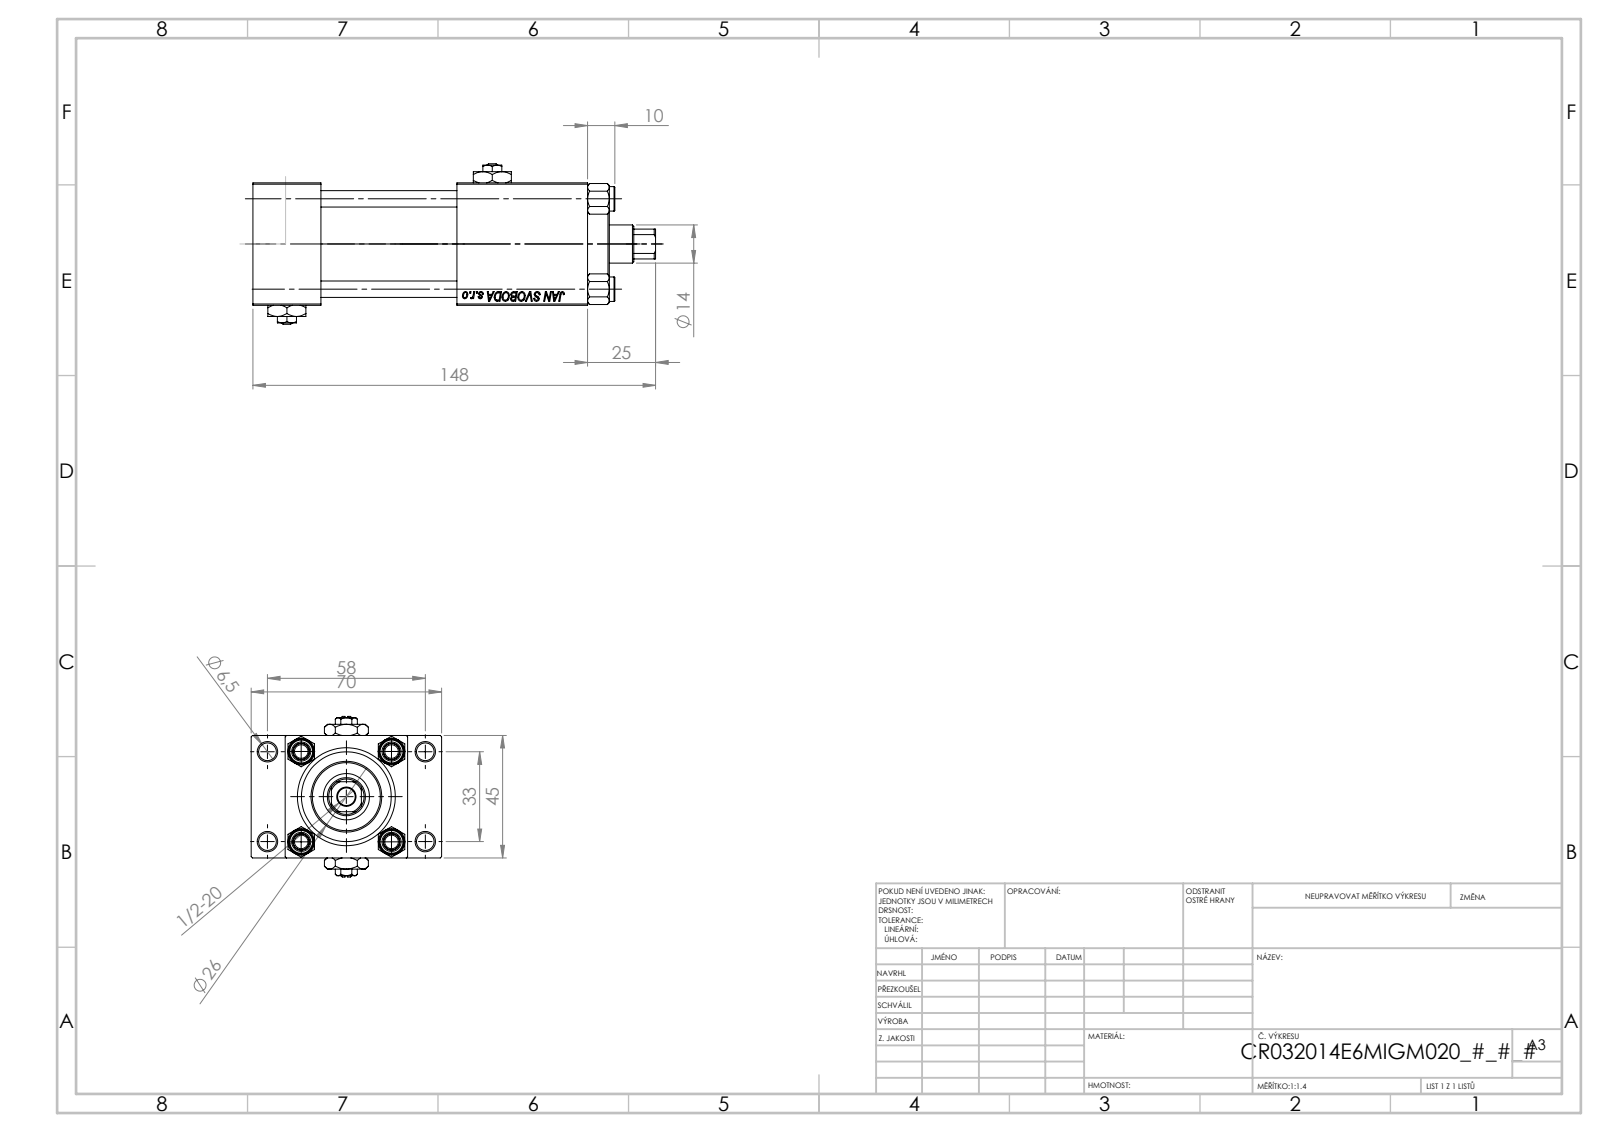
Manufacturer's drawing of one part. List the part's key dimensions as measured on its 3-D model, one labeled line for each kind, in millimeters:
Part name (STEP PRODUCT): V215_VC_A; V215CR_VCP_E; V215CR_TYCINKA_E; Zatka_pro_OIL_PORT (+2 more)
STEP written by: SolidWorks 2019 (CONFIG_CONTROL_DESIGN)
Units: millimetres
Bodies: 13 solids, 1229 faces (542 planar, 93 cylindrical, 594 other)
Overall size (bounding box): 148 × 70 × 59
Volume: 219 579 mm³ · Surface area: 78 015 mm²
Round holes (diameter × count): ⌀6.5 ×5, ⌀6 ×4, ⌀7 ×3, ⌀13.16 ×3, ⌀20 ×3, ⌀14 ×1, ⌀17 ×1, ⌀24 ×1, ⌀32 ×1, ⌀33 ×1
Round bosses / shafts (diameter × count): ⌀9 ×4, ⌀38 ×1, ⌀26 ×1
Partial cylindrical surfaces — rounded edges, fillets, slot ends (radius × count): R6.5 ×1
Main face-to-face distances: 45, 25, 12.5, 57.5, 123, 98, 50, 75, 48, 94.3
Hole centre spacings: 12.4, 23.48, 33.2, 33.37, 35.35, 45.6, 56.35, 33
